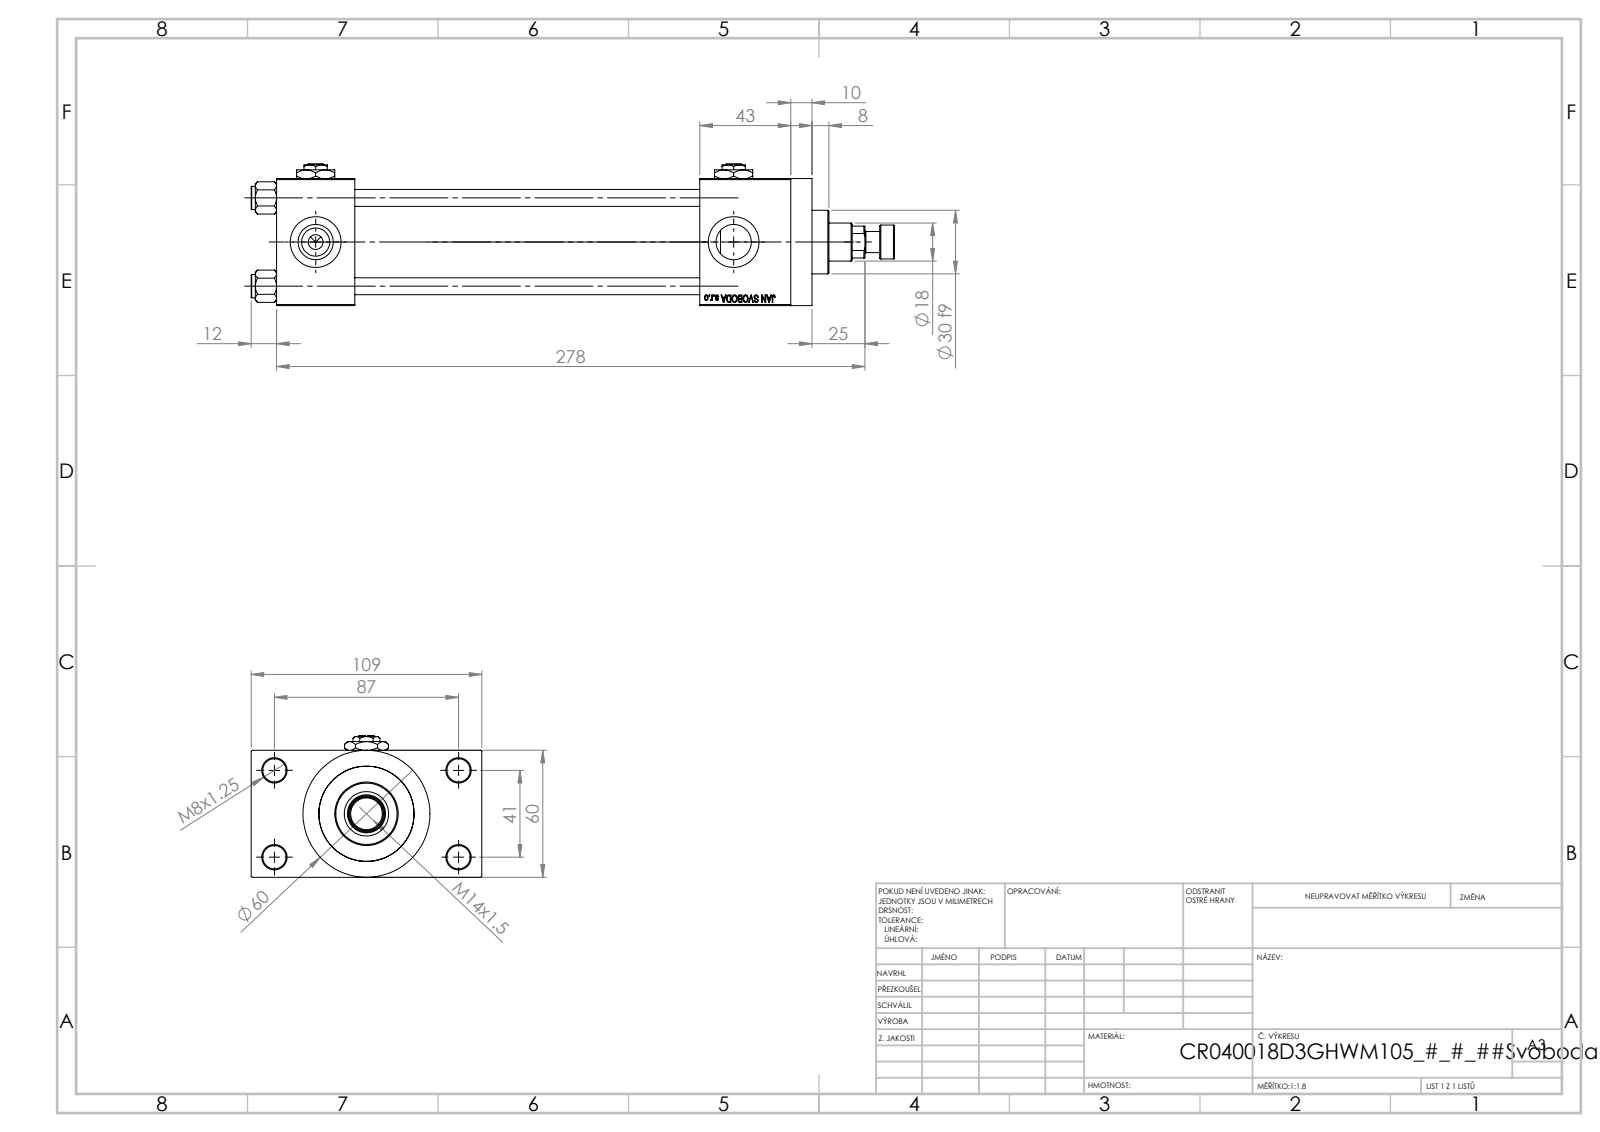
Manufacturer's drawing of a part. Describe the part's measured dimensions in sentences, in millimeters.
The part is named "V215_VC_A; V215CR_D_TYCINKA; V215CR_ROD_END_W; NUT_M5_D (+3 more)". Its 3-D file was written by "SolidWorks 2019 (CONFIG_CONTROL_DESIGN)". It is 14 solids with 1218 faces: 549 planar, 103 cylindrical and 566 other. Overall it measures 304 by 109 by 67 millimeters. Its volume is 602 677 cubic millimeters and its surface area 171 030 square millimeters. Round holes: 4 of diameter 8, 4 of diameter 11, 4 of diameter 16.66, 4 of diameter 24, 3 of diameter 7, 1 of diameter 8.5, 1 of diameter 18, 1 of diameter 21, 1 of diameter 31, 1 of diameter 40, 1 of diameter 45. Round bosses or shafts: 4 of diameter 11, 1 of diameter 60, 1 of diameter 46, 1 of diameter 30, 1 of diameter 16, 1 of diameter 10. Partial cylindrical surfaces (rounded edges, fillets, slot ends): 1 of radius 8.5. The main face-to-face distances are 60, 24.5, 163, 84.5, 37, 200, 43, 243, 206, 10. The hole center spacings are 22.65, 29.49, 41.7, 47.15, 48.09, 64.35, 76.49, 41.
